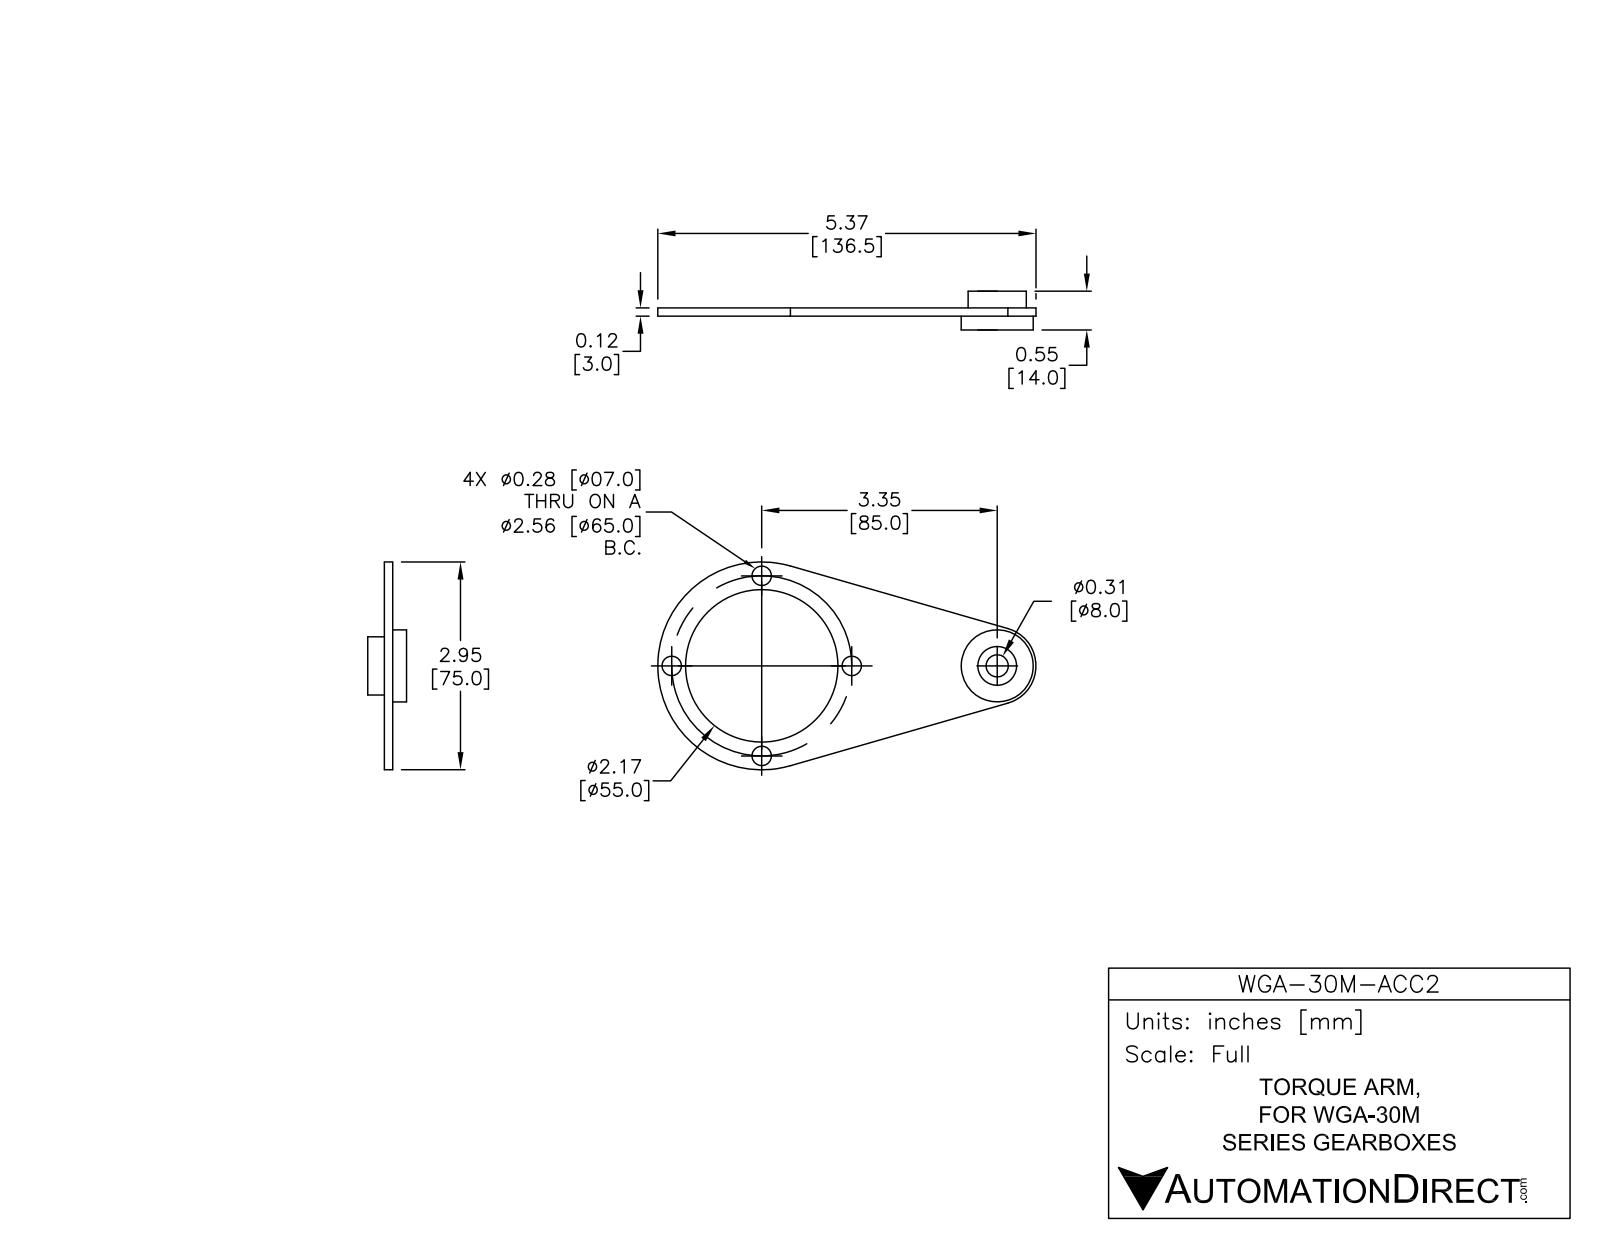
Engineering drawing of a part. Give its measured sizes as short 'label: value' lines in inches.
name: WGA-30M-ACC2
written by: SolidWorks 2014 (AUTOMOTIVE_DESIGN)
unit: in
bodies: 4 solids, 38 faces (10 planar, 28 cylindrical, 0 other)
size: 5.374 × 2.953 × 0.551
volume: 1.076 in³; area: 22.15 in²
holes: 4× ⌀0.276, 1× ⌀0.315, 1× ⌀0.551, 1× ⌀2.165
bosses: 1× ⌀1.024, 1× ⌀0.827
rounds: 1× R0.551, 1× R1.476
face distances: 0.118, 0.315, 0.197, 0.236, 0.354, 0.551
hole spacings: 1.28, 1.809, 2.559, 3.583, 2.067, 3.346, 4.626
